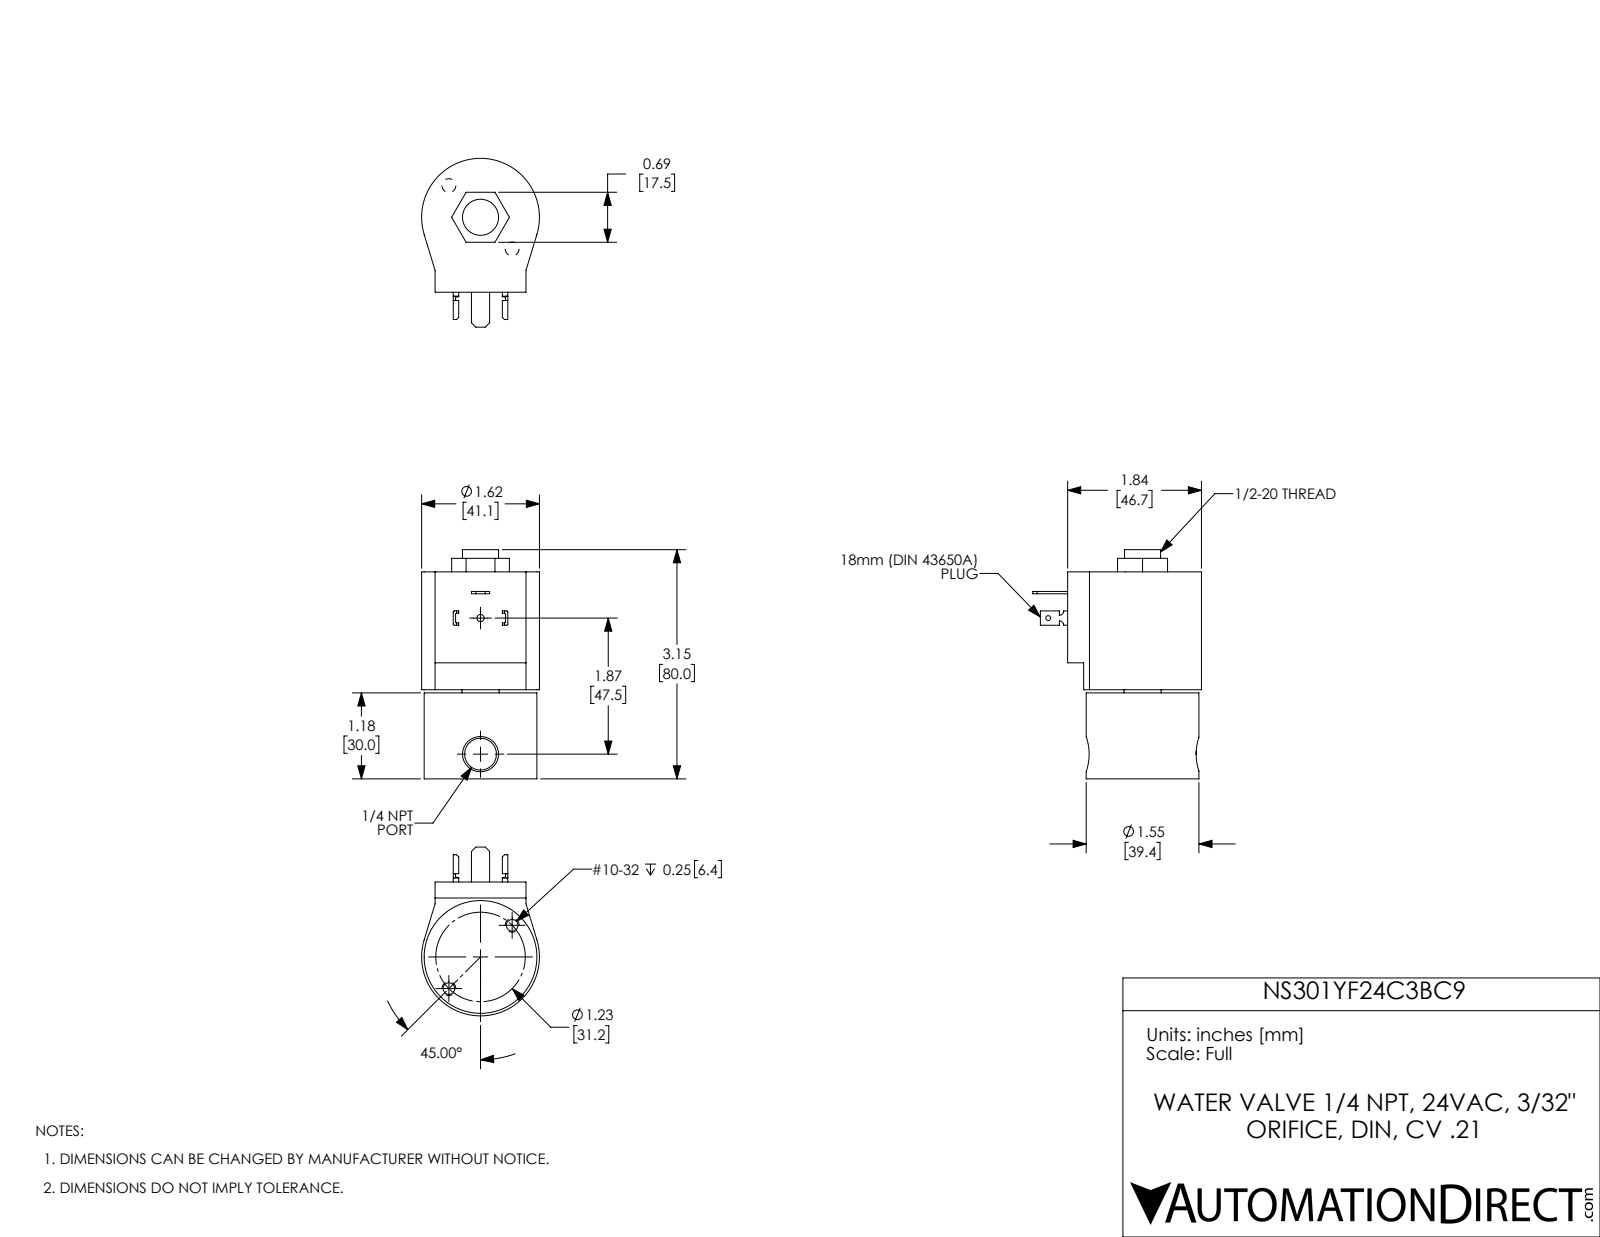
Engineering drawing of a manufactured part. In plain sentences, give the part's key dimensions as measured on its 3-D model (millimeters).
The part is named "NS301YF24C3BC9". Its 3-D file was written by "SolidWorks 2017 (AUTOMOTIVE_DESIGN)". It is 6 solids with 130 faces: 73 planar, 49 cylindrical and 8 other. Overall it measures 80 by 58.9 by 41.1 millimeters. Its volume is 98 760 cubic millimeters and its surface area 21 340 square millimeters. Round holes: 2 of diameter 4, 1 of diameter 1.7, 1 of diameter 2.5, 1 of diameter 11.1, 1 of diameter 12.6, 1 of diameter 13, 1 of diameter 29.3. Round bosses or shafts: 1 of diameter 39.4. Partial cylindrical surfaces (rounded edges, fillets, slot ends): 8 of radius 0.4, 2 of radius 1.5, 1 of radius 20.6. The main face-to-face distances are 72.3, 30, 42.2, 31.1, 1.1, 41.1, 32.7, 2.7, 1.6, 39.6. The hole center spacings are 15.6, 31.2, 47.5.
